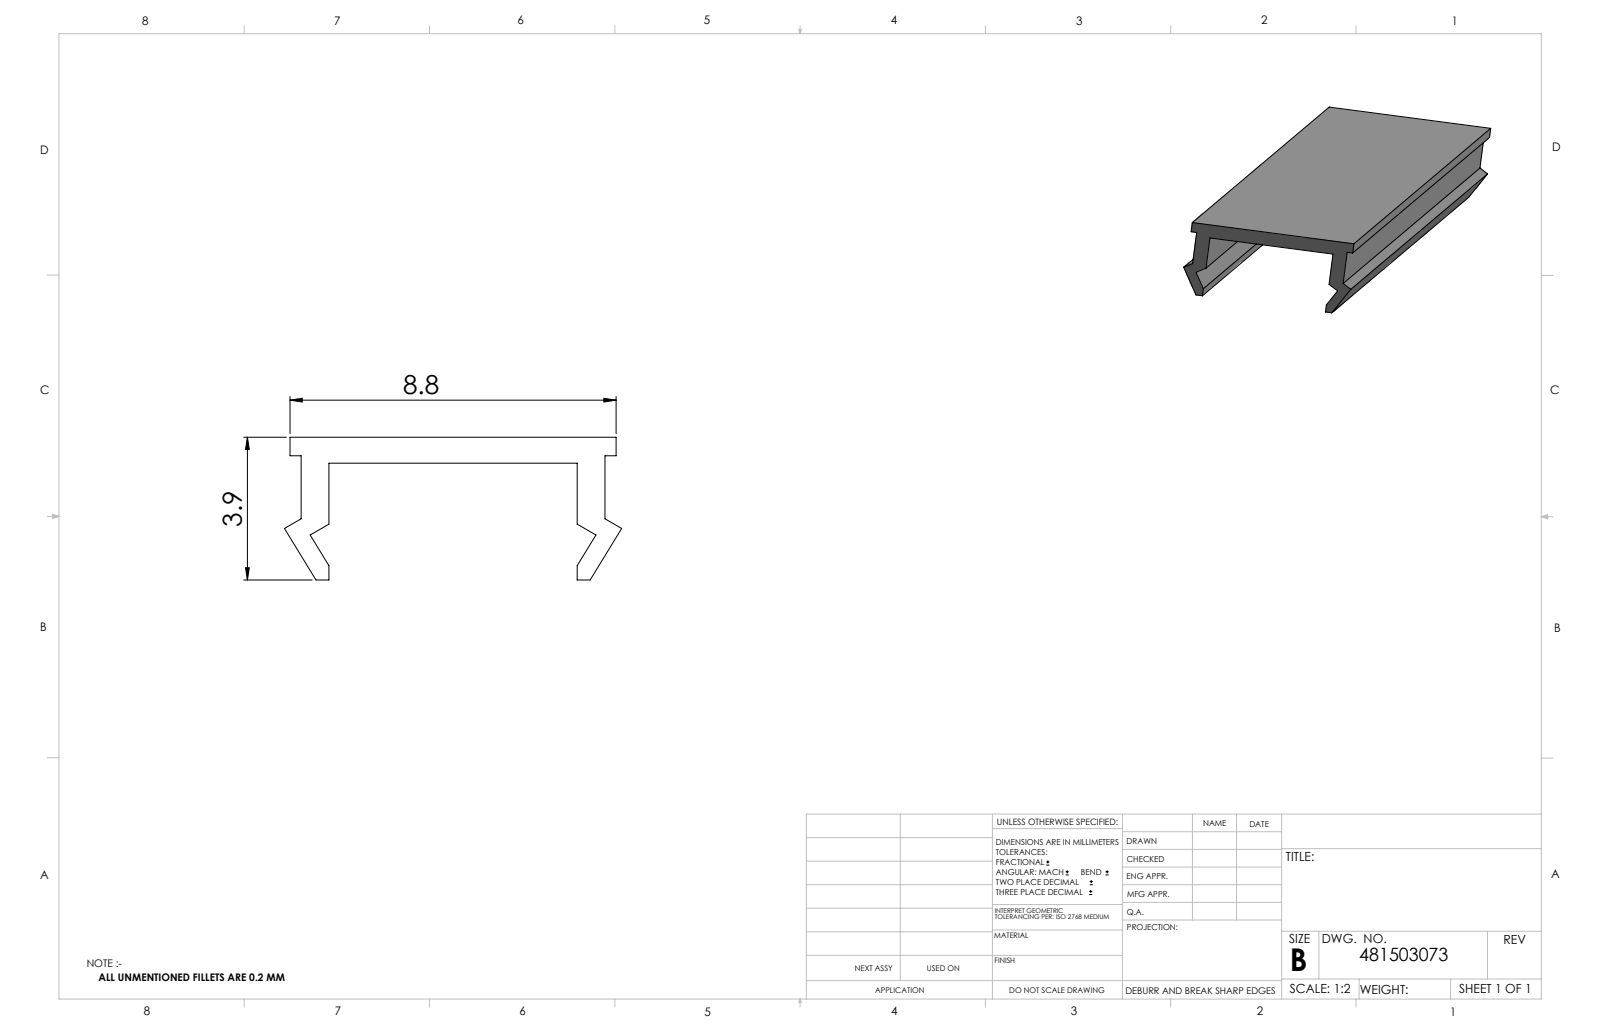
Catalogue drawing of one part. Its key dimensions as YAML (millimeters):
part_name: "481503073_c_1"
step_written_by: "SolidWorks 2014 (CONFIG_CONTROL_DESIGN)"
units: millimeters
bodies: {solids: 1, faces: 24, planar: 24, cylindrical: 0, other: 0}
overall_size: [200, 9.1, 3.85]
volume: 2077
surface_area: 6554
face_to_face_distances: [0.7, 0.5, 0.75, 7.45, 6.7, 8.2, 1.05, 7.75, 8.5, 3.15]
